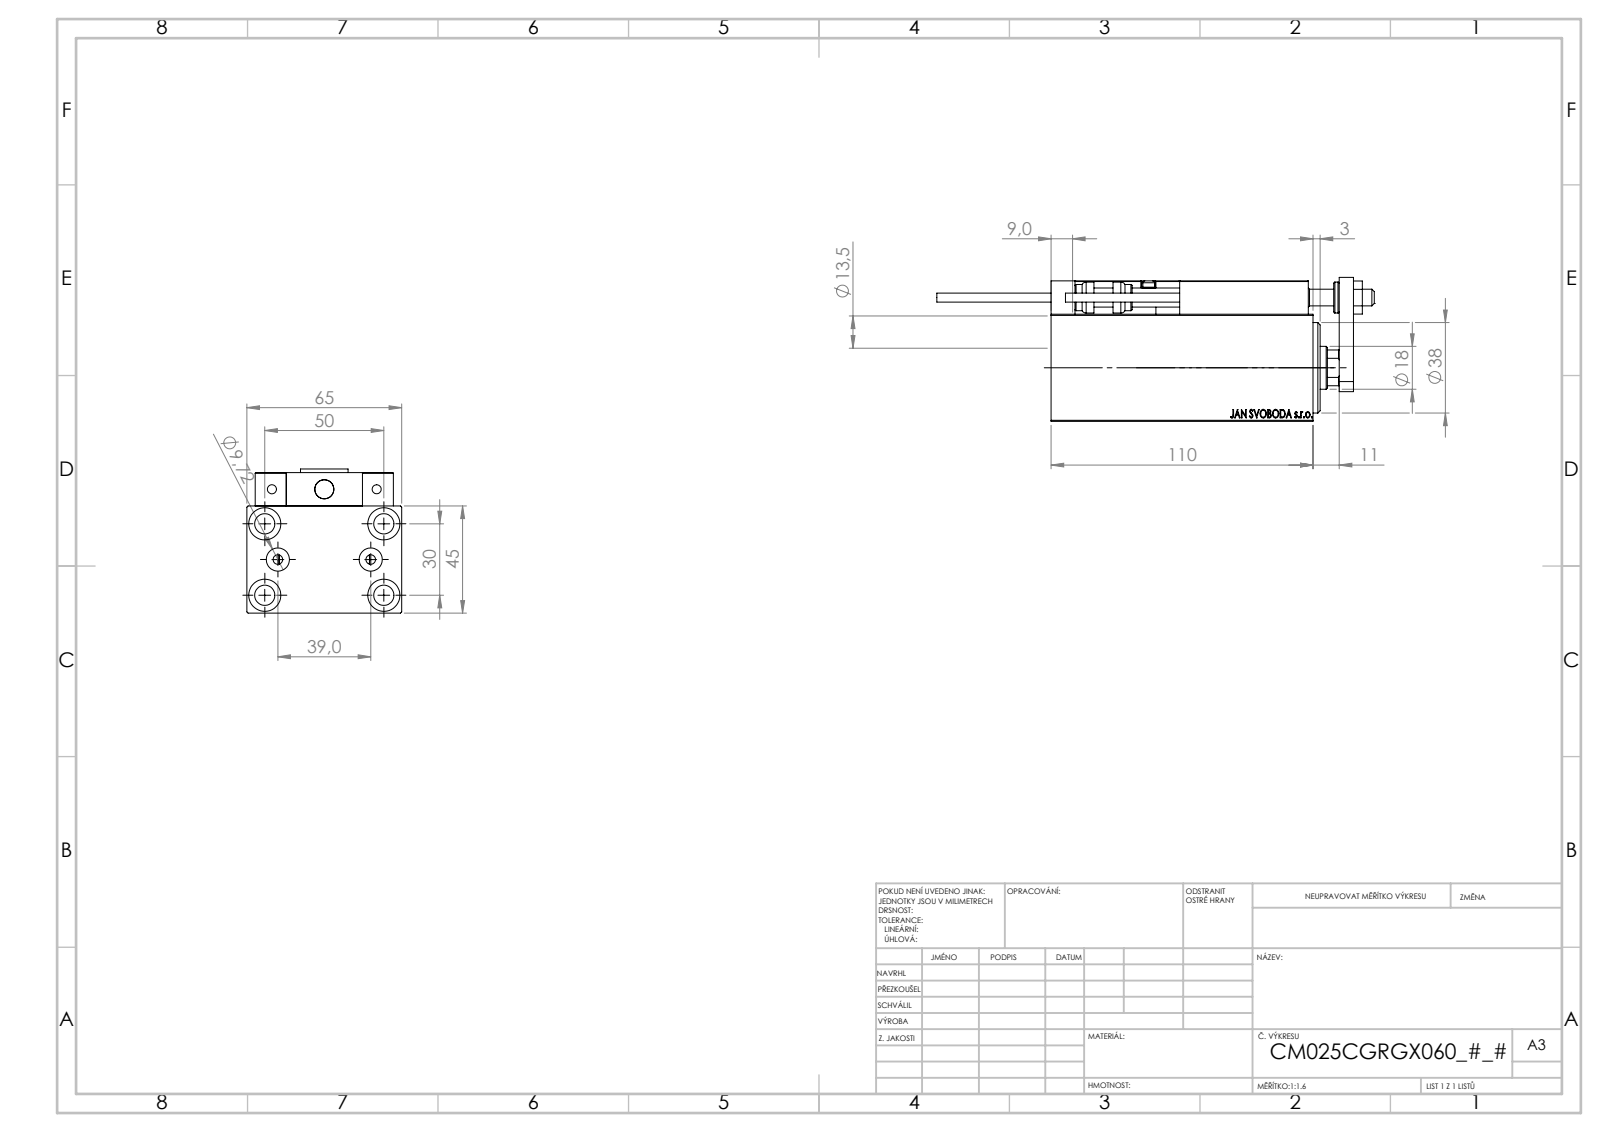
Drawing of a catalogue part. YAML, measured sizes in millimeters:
part_name: "NUT_D12; TYC_L79; V450CM_C_Body; V450CM_C_VCP (+7 more)"
step_written_by: "SolidWorks 2019 (CONFIG_CONTROL_DESIGN)"
units: millimeters
bodies: {solids: 23, faces: 1278, planar: 560, cylindrical: 184, other: 534}
overall_size: [183.7, 65, 60.5]
volume: 323443
surface_area: 90400
round_holes:
  - {diameter: 4, count: 6}
  - {diameter: 8, count: 5}
  - {diameter: 8.5, count: 5}
  - {diameter: 3.2, count: 4}
  - {diameter: 13.5, count: 4}
  - {diameter: 5, count: 2}
  - {diameter: 9.72, count: 2}
  - {diameter: 7, count: 1}
  - {diameter: 14.5, count: 1}
  - {diameter: 18, count: 1}
  - {diameter: 21.5, count: 1}
  - {diameter: 25, count: 1}
round_bosses_or_shafts:
  - {diameter: 5, count: 2}
  - {diameter: 3.8, count: 2}
  - {diameter: 13, count: 1}
  - {diameter: 11, count: 1}
partial_cylinders:
  - {radius: 0.3, count: 30}
  - {radius: 3, count: 2}
  - {radius: 8.5, count: 1}
face_to_face_distances: [45, 65, 14, 6, 59, 3, 7, 13, 5, 121]
hole_center_spacings: [15.98, 29.15, 46.96, 11.37, 19.5, 20, 28.9, 29.59]
